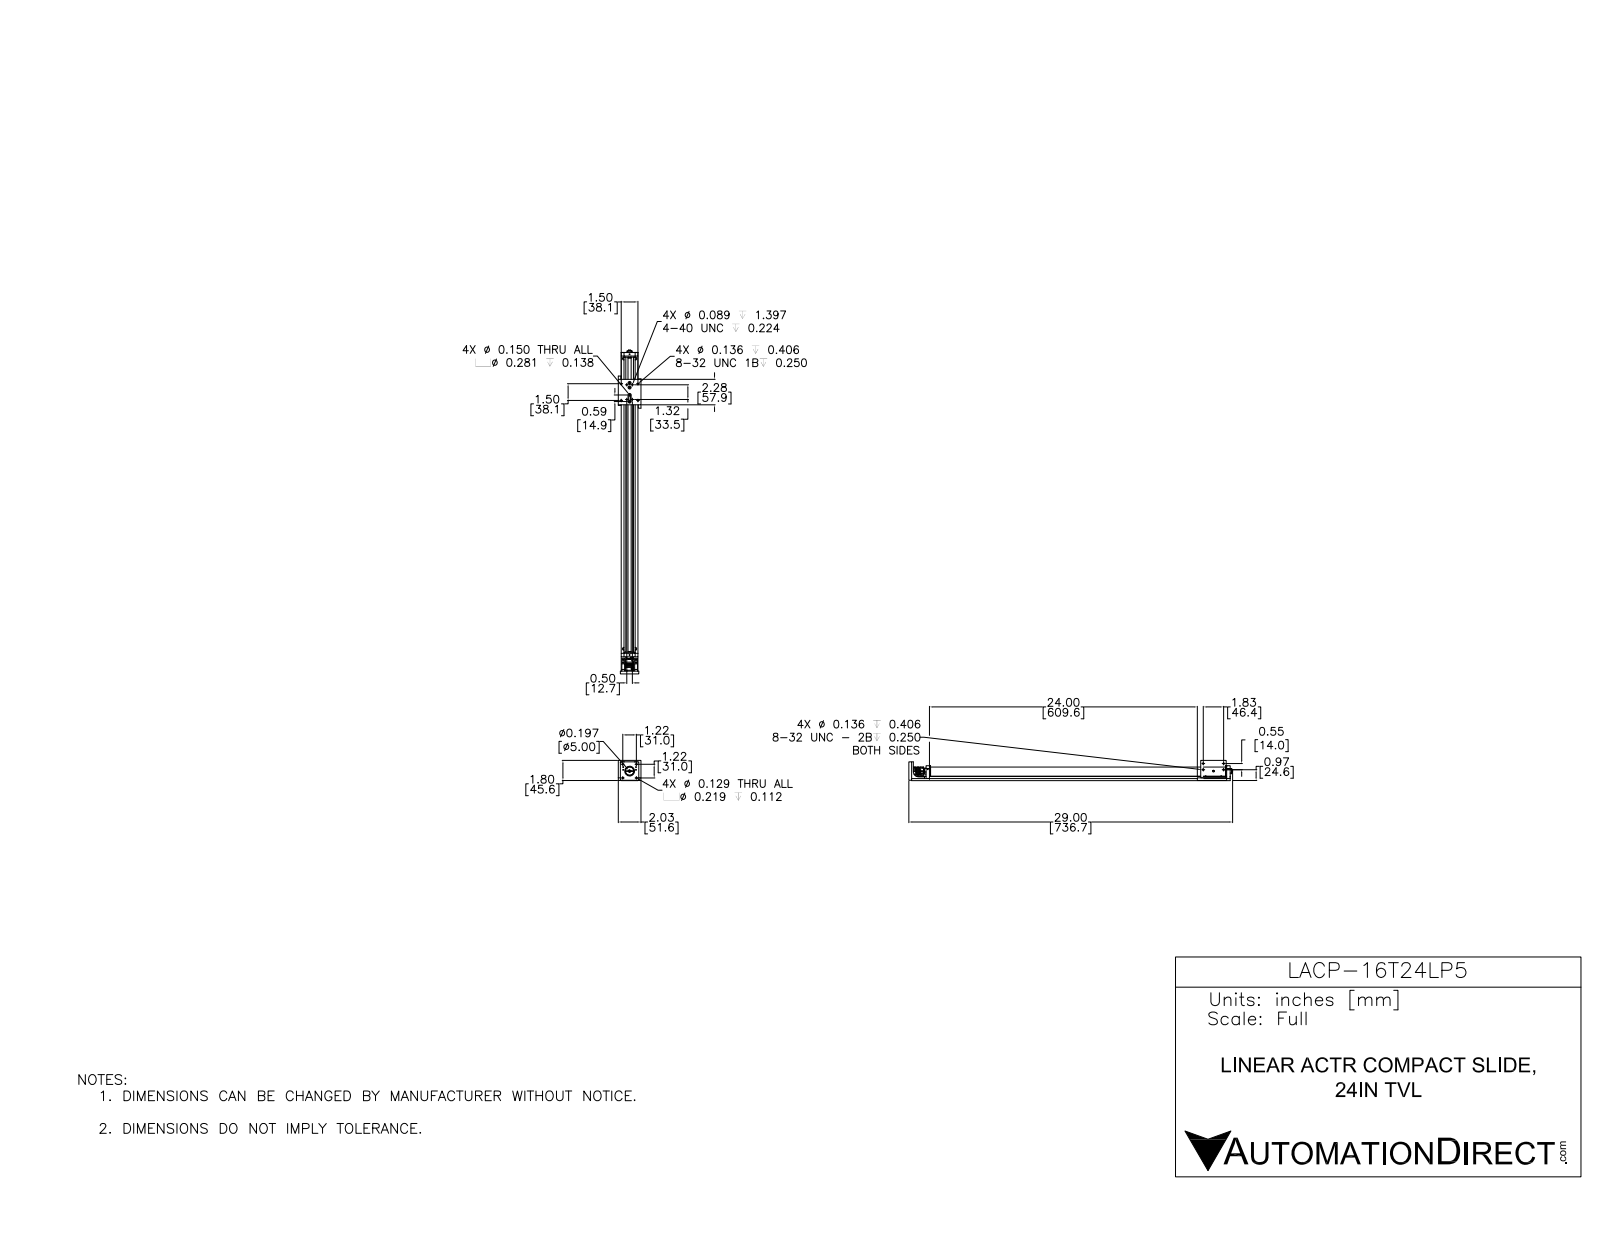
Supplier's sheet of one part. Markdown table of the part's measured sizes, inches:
| quantity | value |
| --- | --- |
| part name | LACP-16TXXLP5-CAR; LACP-16T24LP5; LACP-16T24LP5-RAIL |
| STEP written by | SolidWorks 2016 (AUTOMOTIVE_DESIGN) |
| units | inches |
| bodies | 25 solids, 887 faces (280 planar, 517 cylindrical, 90 other) |
| overall size | 28.995 × 2.03 × 1.812 |
| volume | 31.62 in³ |
| surface area | 351.6 in² |
| round holes (diameter × count) | 0.089 × 16, 0.281 × 16, 0.17 × 14, 0.15 × 9, 0.136 × 8, 0.138 × 7, 0.28 × 7, 0.07 × 4, 0.129 × 4, 0.129 × 4, 0.219 × 4, 0.197 × 3 |
| round bosses / shafts (diameter × count) | 0.157 × 3, 0.15 × 2, 1 × 1, 0.748 × 1, 0.71 × 1, 0.673 × 1, 0.67 × 1, 0.59 × 1 |
| partial cylindrical surfaces (radius × count) | 0.047 × 4, 0.062 × 4, 0.094 × 4, 0.125 × 3, 0.05 × 2, 0.075 × 2, 0.141 × 2, 0.25 × 2 |
| main face-to-face distances | 0.187, 1.219, 1.031, 0.265, 1.765, 1.5, 0.875, 1.155, 0.61, 0.89 |
| hole center spacings | 4.031, 8.016, 4, 12.01, 8, 0.5, 4.123, 12 |
